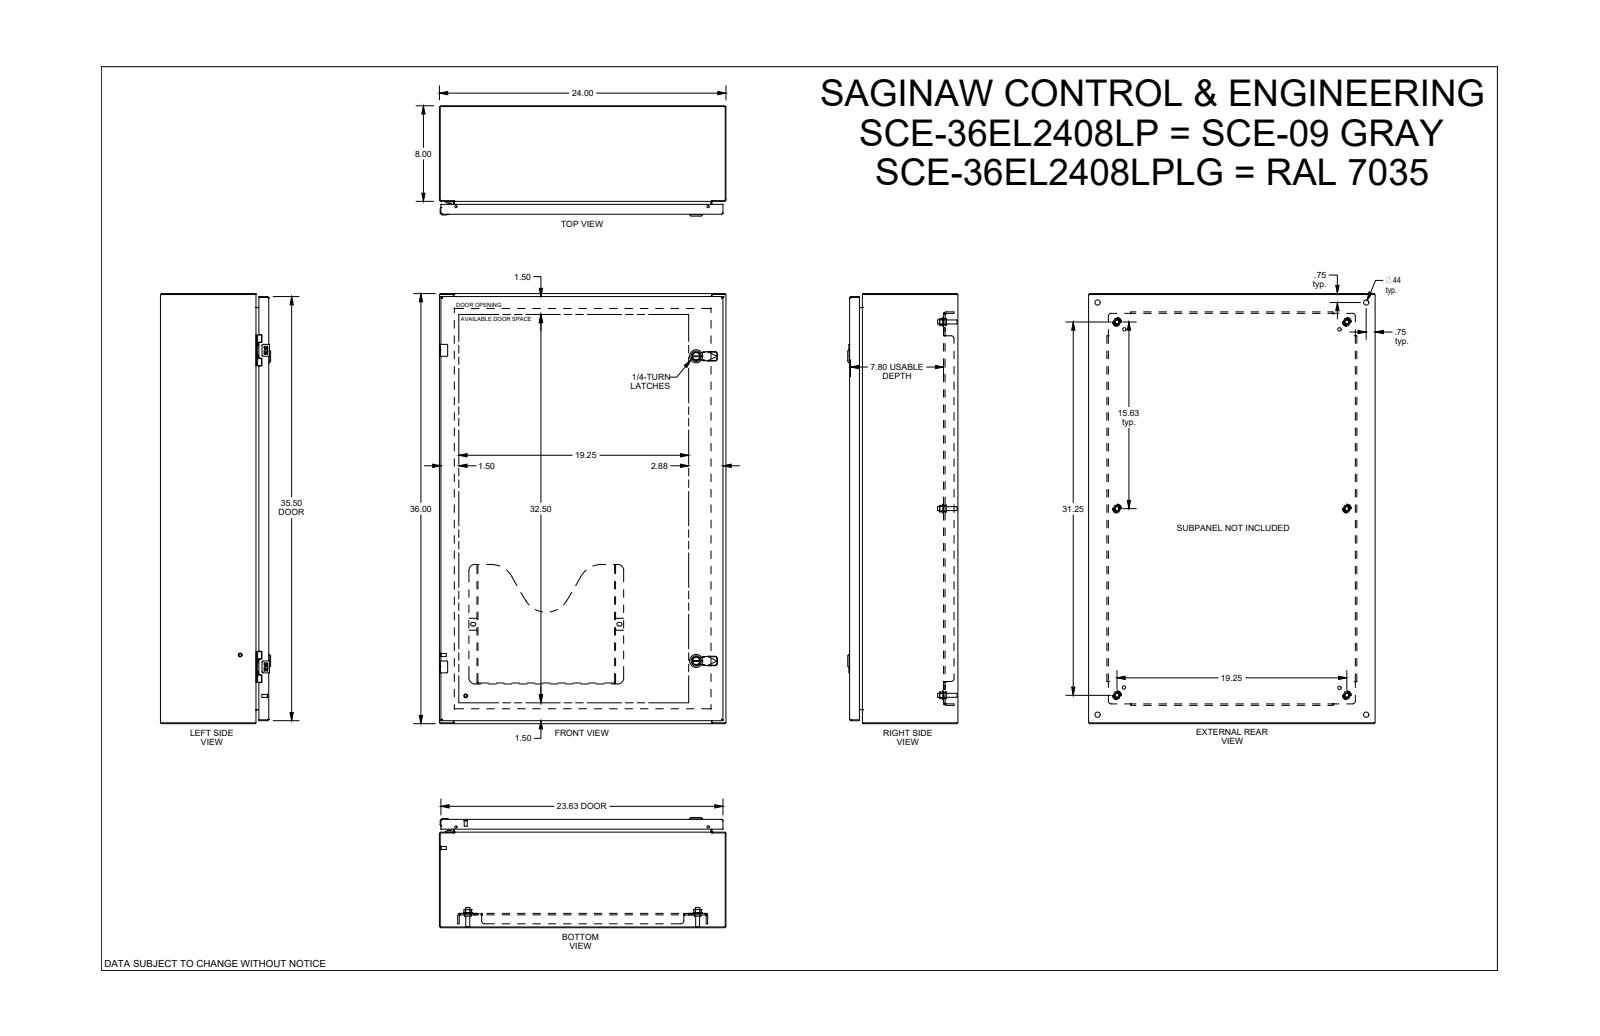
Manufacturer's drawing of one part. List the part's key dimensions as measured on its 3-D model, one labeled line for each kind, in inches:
Part name (STEP PRODUCT): SCE-36EL2408LP
STEP written by: SolidWorks 2021 (AUTOMOTIVE_DESIGN)
Units: inches
Bodies: 51 solids, 2989 faces (1139 planar, 888 cylindrical, 962 other)
Overall size (bounding box): 36 × 24 × 9.23
Volume: 334.7 in³ · Surface area: 8 011 in²
Round holes (diameter × count): ⌀0.367 ×6, ⌀0.5 ×6, ⌀0.172 ×4, ⌀0.205 ×4, ⌀0.244 ×4, ⌀0.266 ×4, ⌀0.281 ×4, ⌀0.375 ×4, ⌀0.437 ×4, ⌀0.04 ×2, ⌀0.188 ×2, ⌀0.197 ×2
Round bosses / shafts (diameter × count): ⌀0.366 ×6, ⌀0.332 ×6, ⌀0.17 ×6, ⌀0.25 ×4, ⌀0.248 ×4, ⌀0.24 ×4, ⌀0.196 ×3, ⌀1.102 ×2
Partial cylindrical surfaces — rounded edges, fillets, slot ends (radius × count): R0.012 ×56, R0.01 ×40, R0.015 ×24, R0.02 ×20, R0.04 ×17, R0.06 ×13, R0.029 ×12, R0.1 ×12
Main face-to-face distances: 0.075, 0.06, 9.073, 8.998, 9.013, 8.938, 1.2, 7.873, 1, 0.125
Hole centre spacings: 0.985, 15.625, 17.326, 26.5, 15.019, 0.02, 0.493, 0.494
